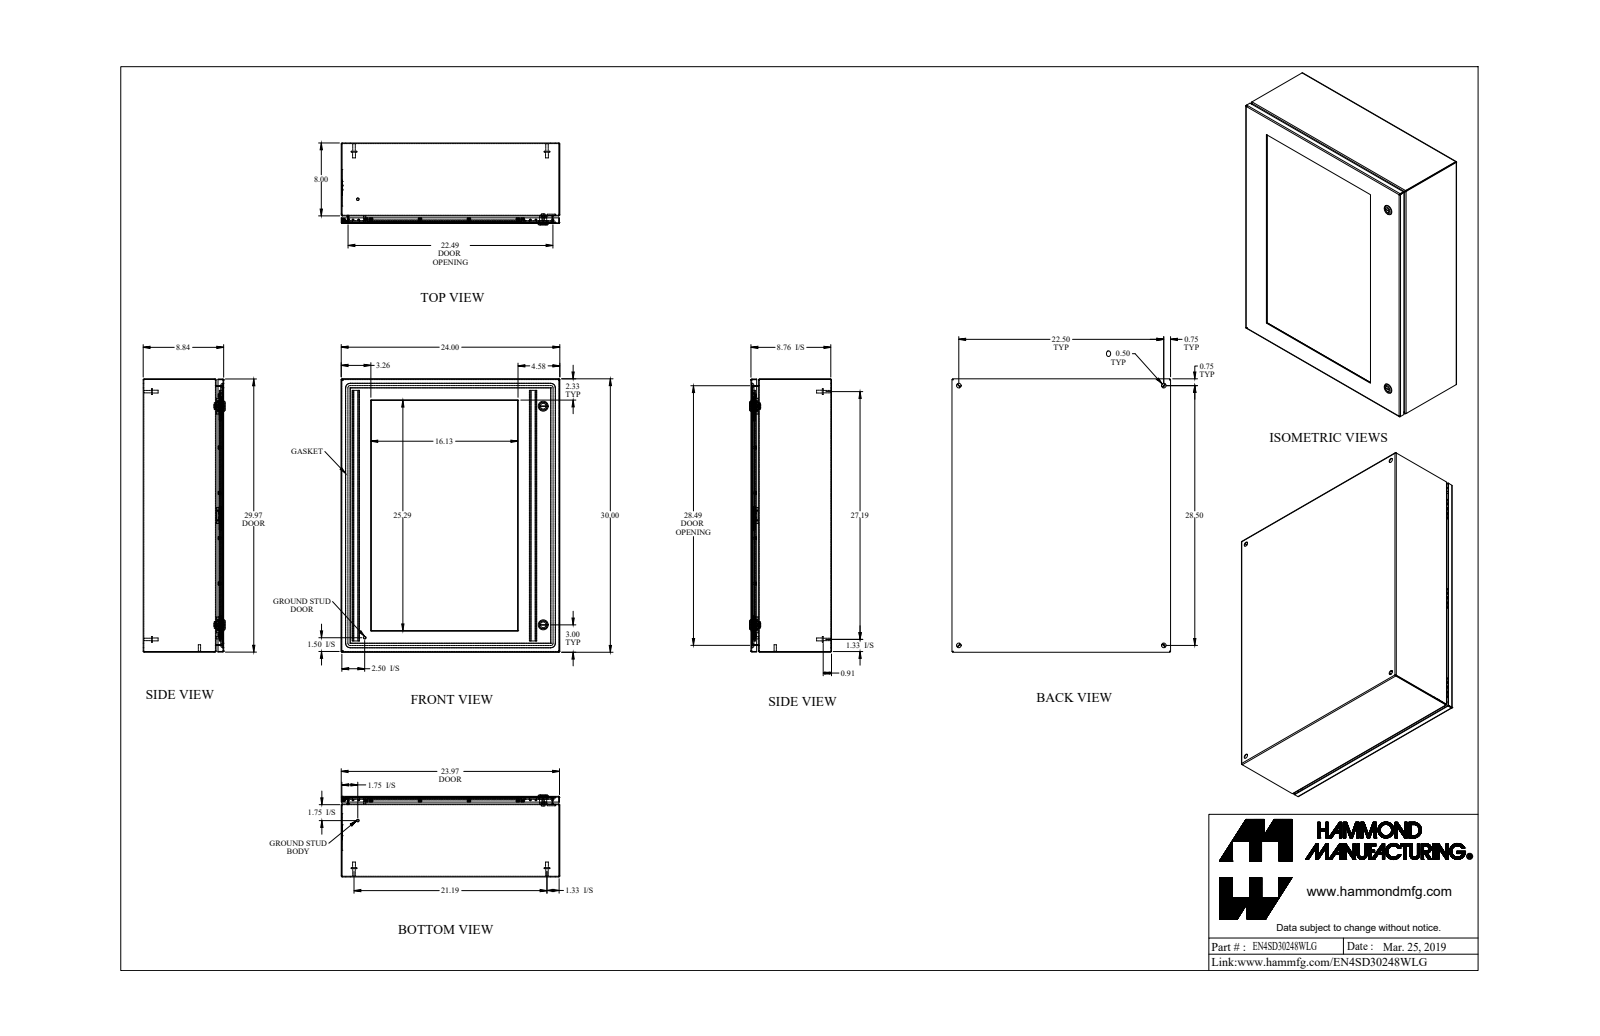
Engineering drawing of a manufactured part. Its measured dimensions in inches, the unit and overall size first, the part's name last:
Units: inches
Overall size (bounding box): 30 × 24 × 8.997
Round holes (diameter × count): ⌀0.13 ×20, ⌀0.25 ×20, ⌀0.5 ×4, ⌀0.232 ×2, ⌀0.625 ×2, ⌀0.785 ×2, ⌀0.172 ×1, ⌀0.24 ×1, ⌀0.242 ×1
Round bosses / shafts (diameter × count): ⌀0.226 ×21, ⌀0.368 ×20, ⌀0.164 ×20, ⌀0.625 ×4, ⌀0.313 ×4, ⌀0.27 ×4, ⌀1.1 ×2, ⌀0.525 ×2
Partial cylindrical surfaces — rounded edges, fillets, slot ends (radius × count): R0.036 ×20, R0.108 ×20, R0.043 ×12, R0.081 ×12, R0.125 ×12, R0.382 ×12, R19.003 ×8, R0.006 ×6
Main face-to-face distances: 0.072, 8.765, 8.693, 8.443, 0.25, 8.515, 23.928, 29.928, 0.322, 8.837
Hole centre spacings: 9.95, 19.822, 4.975, 17.144, 17.851, 5.372, 5.372, 14.925
Volume: 281.4 in³ · Surface area: 5 826 in²
Bodies: 80 solids, 1652 faces (833 planar, 511 cylindrical, 308 other)
Part name (STEP PRODUCT): EN4SD30248WLG_Default
STEP written by: SolidWorks 2019 (CONFIG_CONTROL_DESIGN)
